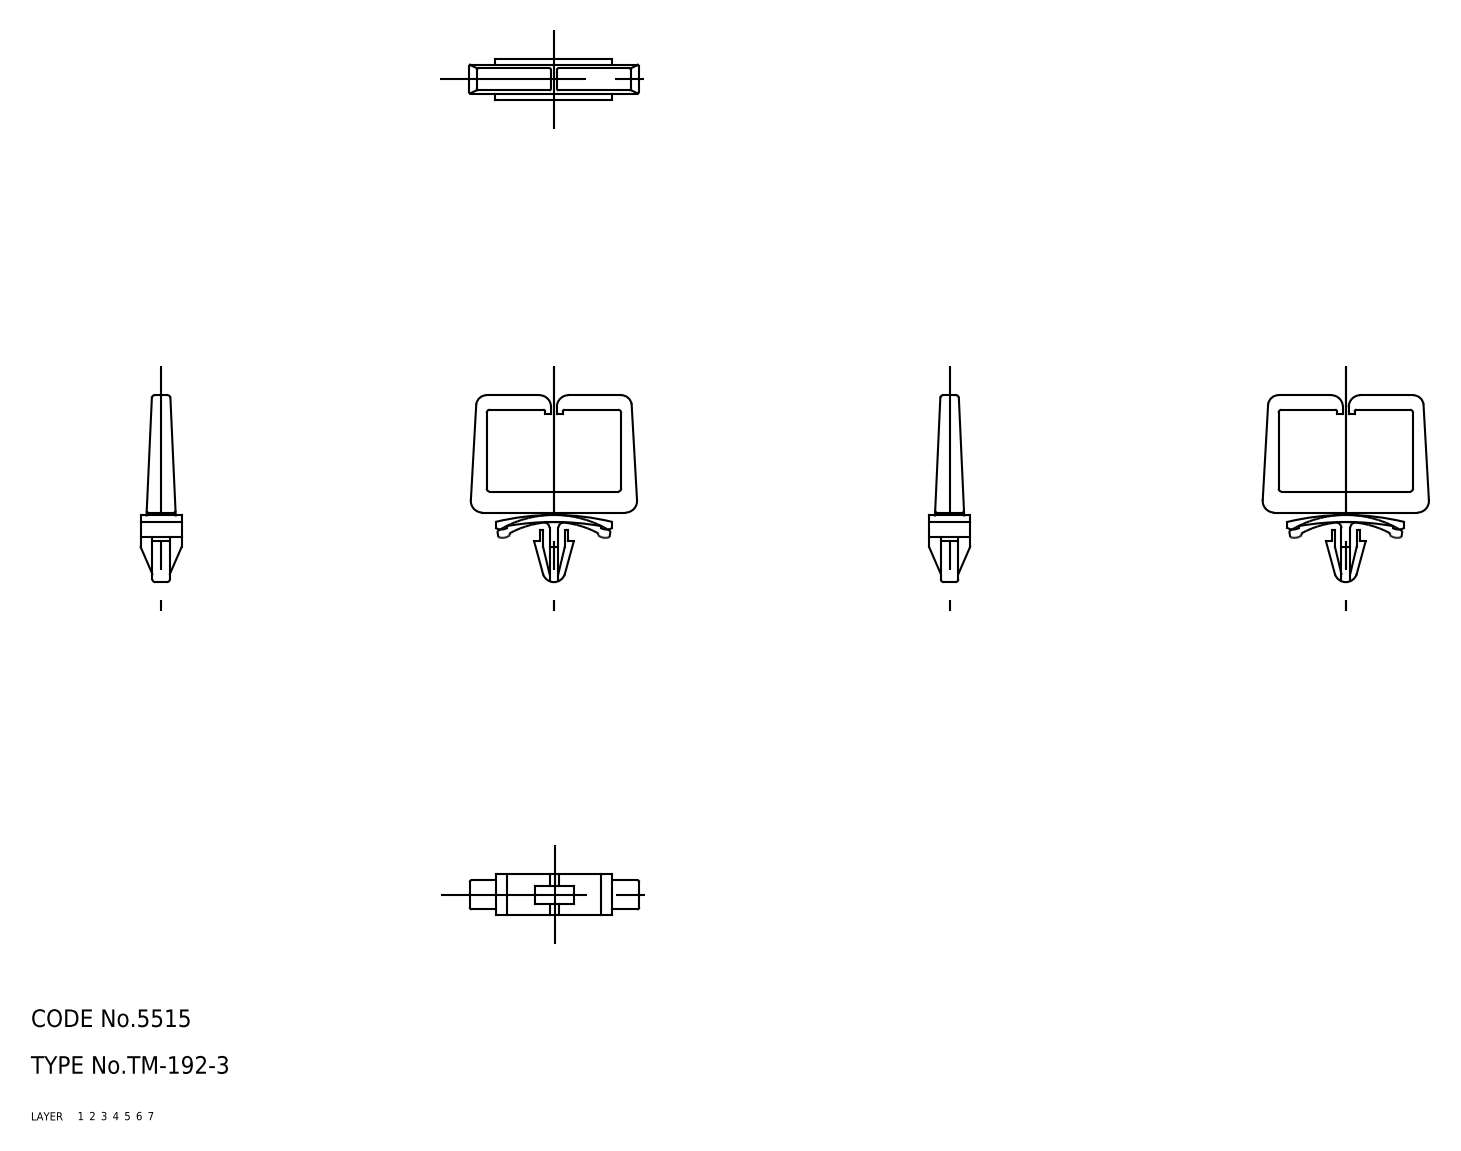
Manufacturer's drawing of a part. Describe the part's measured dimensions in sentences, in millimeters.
The part is named "clip". Its 3-D file was written by "CADfix (AUTOMOTIVE_DESIGN)". It is 1 solid with 118 faces: 0 planar, 0 cylindrical and 118 other. Overall it measures 32 by 28.46 by 7 millimeters. Its volume is 1 236 cubic millimeters and its surface area 1 643 square millimeters.
